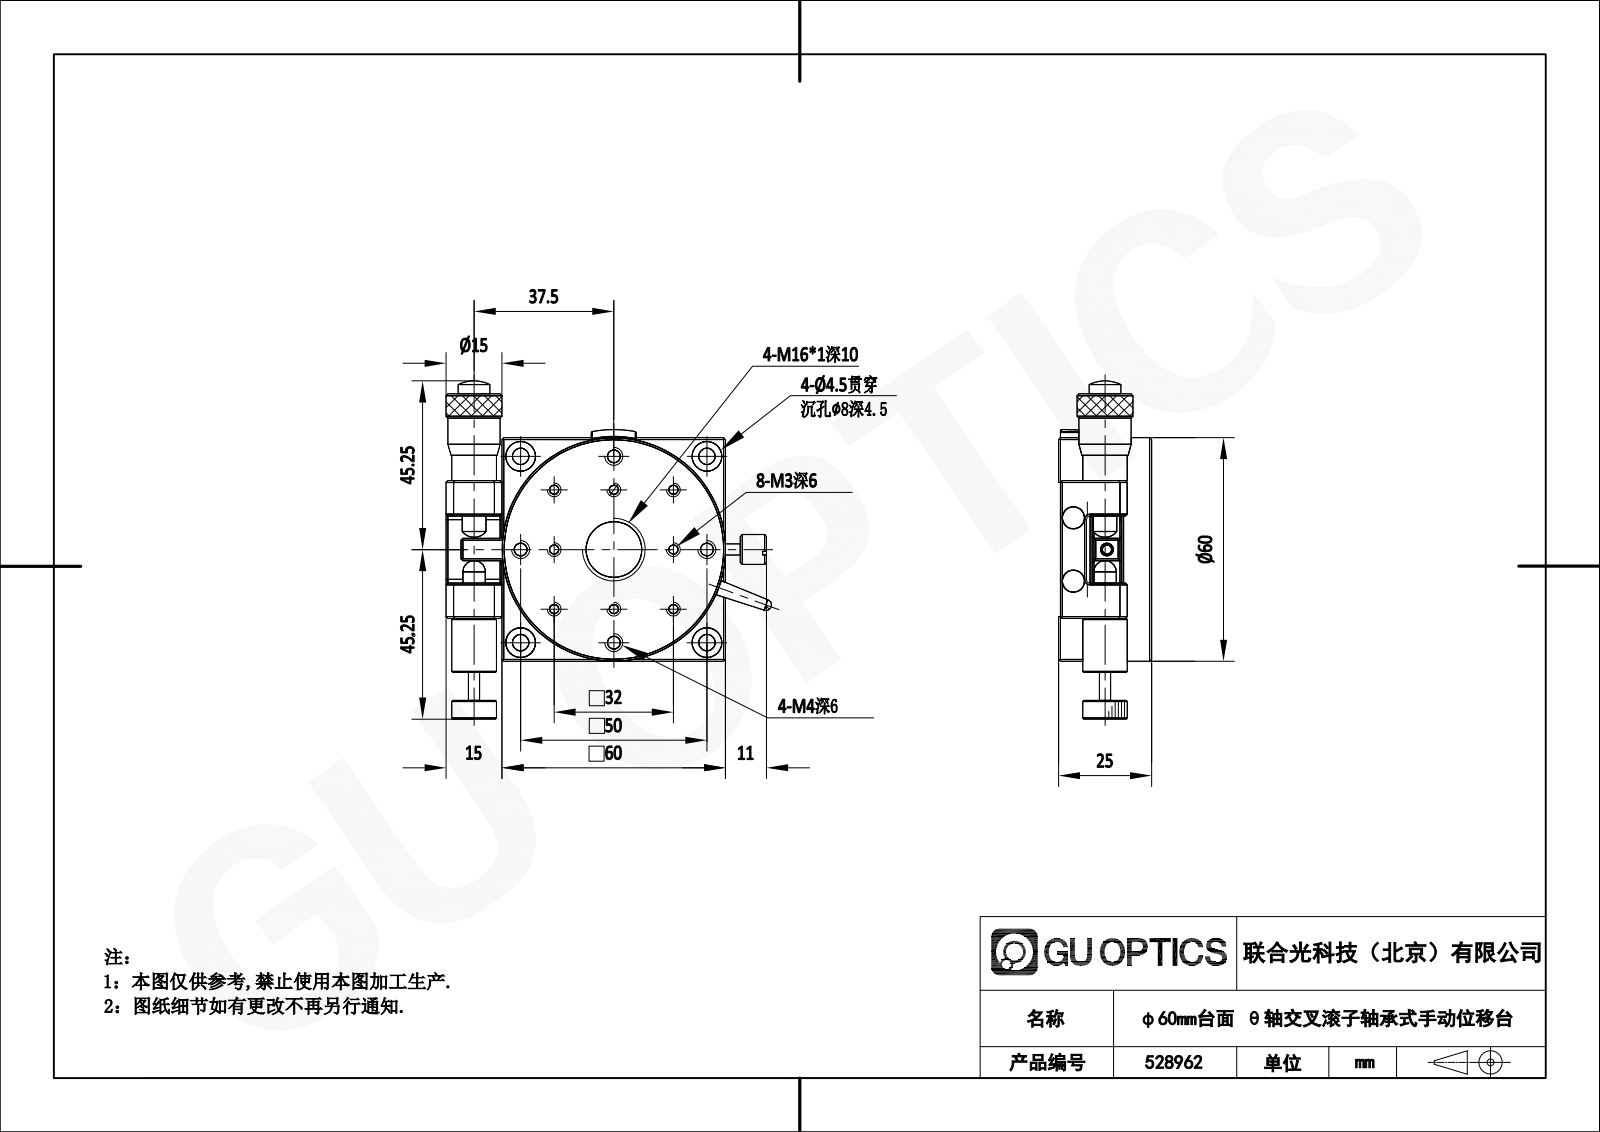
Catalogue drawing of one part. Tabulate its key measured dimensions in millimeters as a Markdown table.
| quantity | value |
| --- | --- |
| part name | 528962 |
| STEP written by | SolidWorks 2020 (CONFIG_CONTROL_DESIGN) |
| units | millimeters |
| bodies | 0 solids, 2042 faces (70 planar, 429 cylindrical, 1543 other) |
| overall size | 103.89 × 91.08 × 25.16 |
| round holes (diameter × count) | 2.46 × 5, 3.24 × 4, 2.46 × 3, 3 × 2, 6 × 1, 6.35 × 1, 8 × 1, 9.5 × 1, 12 × 1, 14.92 × 1, 60 × 1 |
| round bosses / shafts (diameter × count) | 8 × 4, 4.5 × 4, 58 × 1, 15.64 × 1, 14.44 × 1, 12 × 1, 10.8 × 1 |
| partial cylindrical surfaces (radius × count) | 30.5 × 1, 33 × 1 |
| main face-to-face distances | 12.8, 12, 24.8, 8, 4, 60, 9, 17, 6, 8.8 |
| hole center spacings | 16, 18.36, 22.63, 29.68, 35.78, 44.01, 32, 9 |
